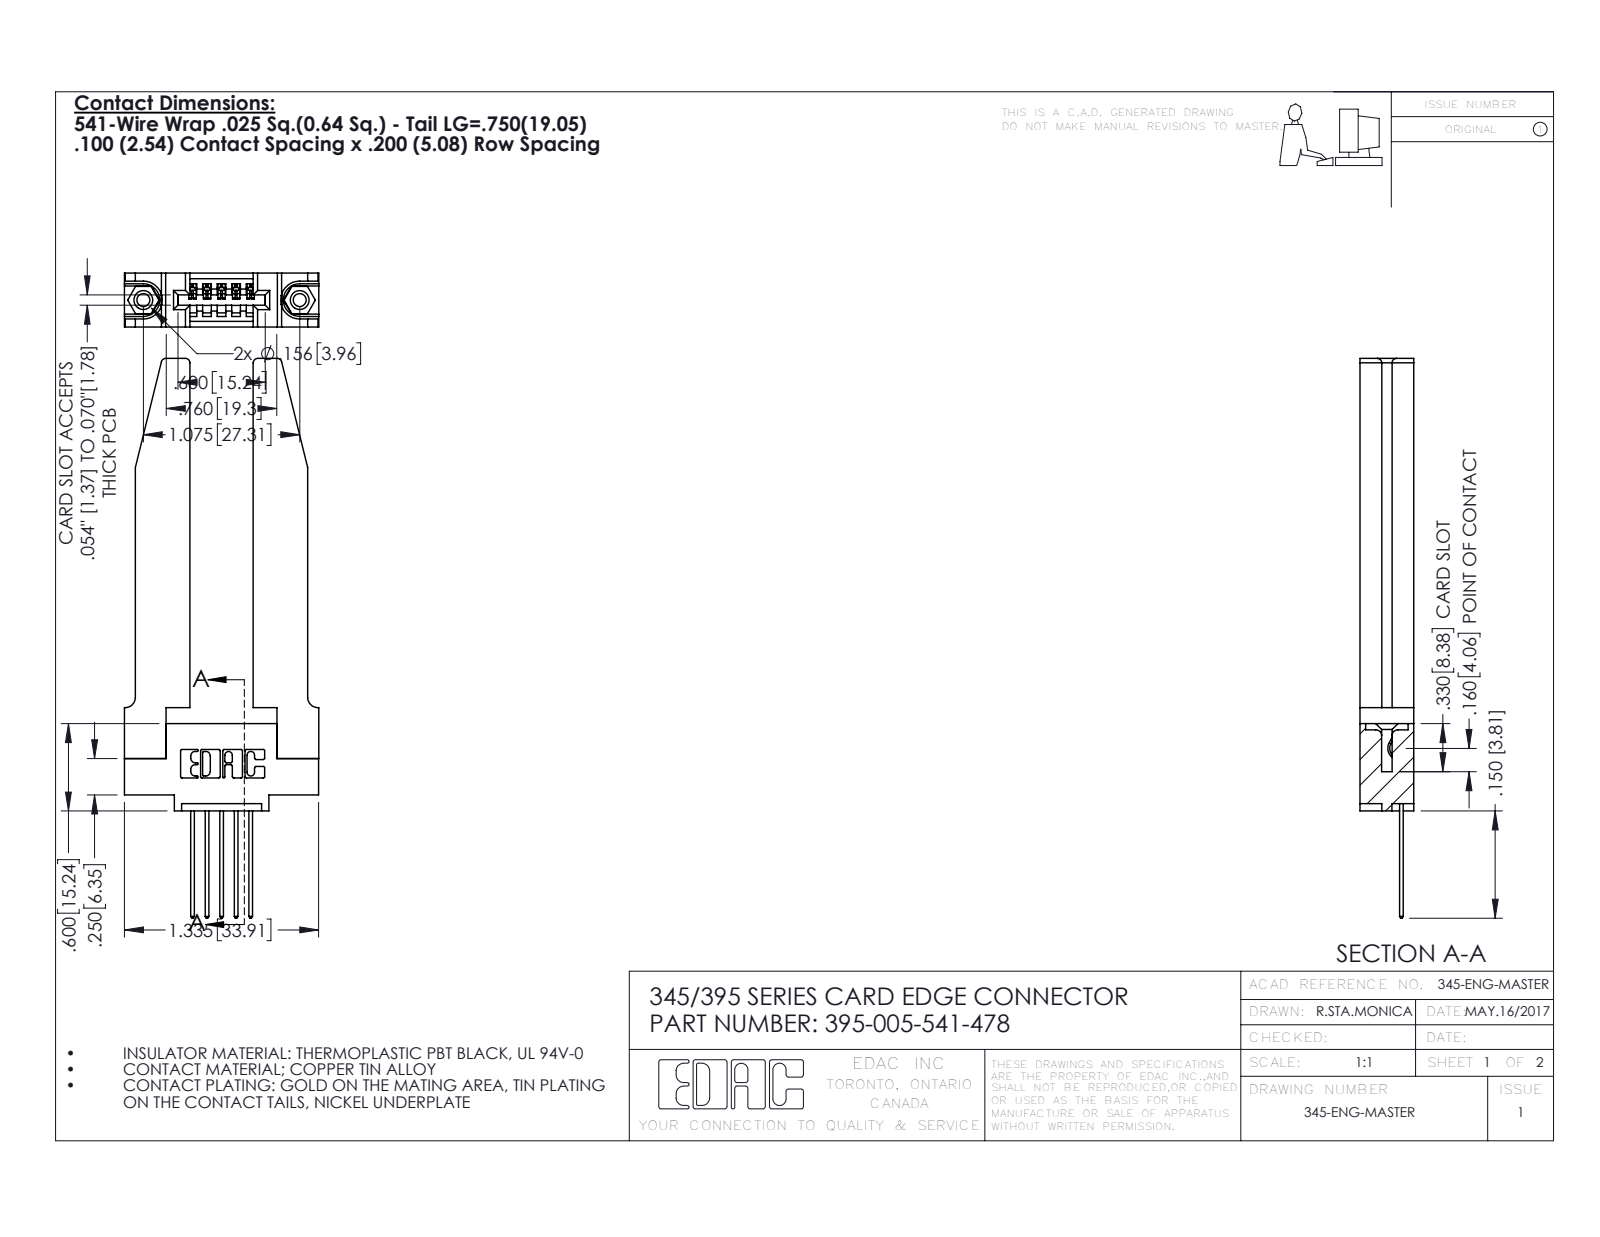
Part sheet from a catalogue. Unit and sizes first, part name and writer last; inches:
Units: inches
Overall size (bounding box): 3.847 × 1.336 × 0.37
Round holes (diameter × count): ⌀0.089 ×2, ⌀0.125 ×2, ⌀0.156 ×2, ⌀0.064 ×1
Round bosses / shafts (diameter × count): ⌀0.155 ×2
Partial cylindrical surfaces — rounded edges, fillets, slot ends (radius × count): R0.01 ×22, R0.006 ×10, R0.01 ×10, R0.03 ×8, R0.007 ×6, R0.031 ×6, R0.026 ×3, R0.031 ×2
Main face-to-face distances: 0.37, 0.15, 0.22, 0.435, 0.148, 0.072, 0.298, 0.077, 0.2, 0.071
Hole centre spacings: 0.27, 0.847, 1.075
Volume: 0.649 in³ · Surface area: 16.01 in²
Bodies: 10 solids, 654 faces (426 planar, 176 cylindrical, 52 other)
Part name (STEP PRODUCT): 345-220-078_345-220-078; 345-292-001_345-293-141; 395-005-541-478; 345 Part_0.110 Offset - 0.156 Dia-TH (+1 more)
STEP written by: SolidWorks 2016 (CONFIG_CONTROL_DESIGN)
